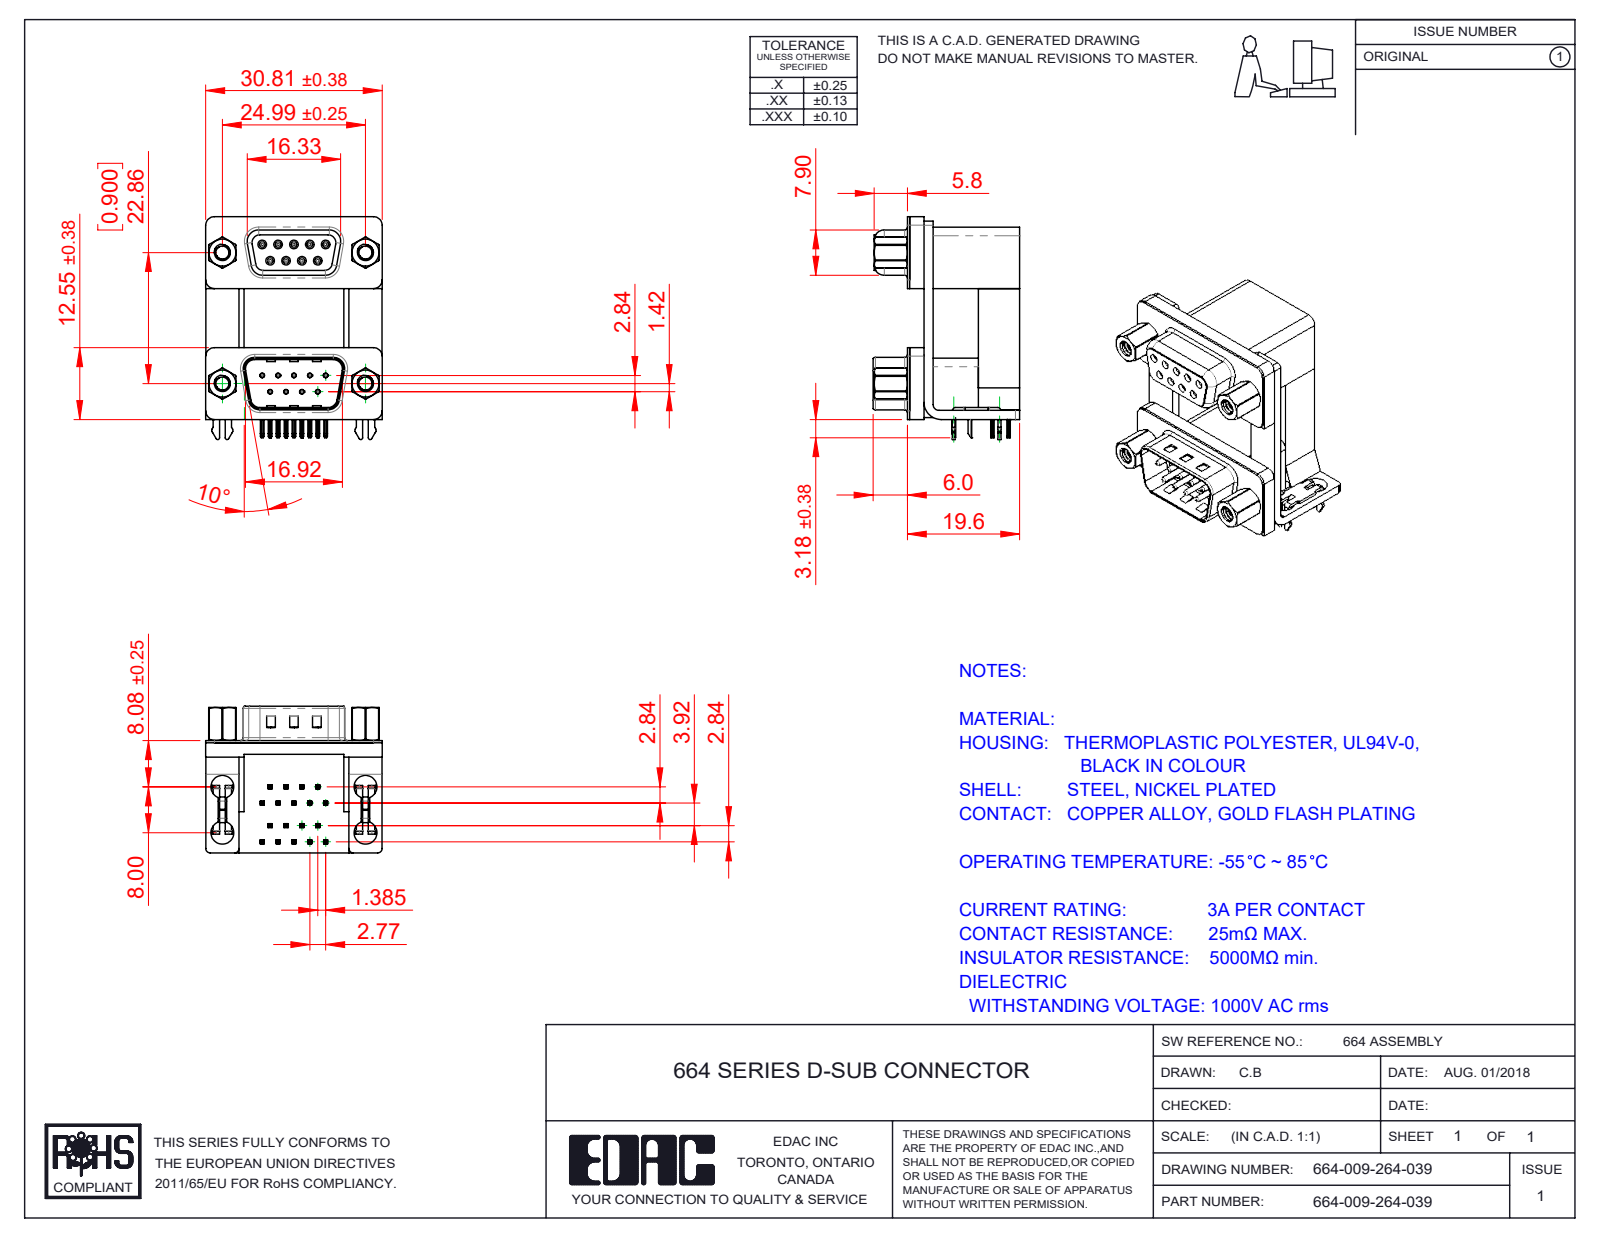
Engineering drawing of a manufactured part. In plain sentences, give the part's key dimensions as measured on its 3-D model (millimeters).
The part is named "664 Contact Bottom Lower; 664 2 Prong Board Lock_3; 664-009-264-039; 664 4-40 Hex Standoff 5 (+8 more)". Its 3-D file was written by "SolidWorks 2020 (CONFIG_CONTROL_DESIGN)". It is 35 solids with 2933 faces: 1409 planar, 889 cylindrical and 635 other. Overall it measures 38.91 by 30.81 by 25.6 millimeters. Its volume is 11 747 cubic millimeters and its surface area 14 269 square millimeters. Round holes: 18 of diameter 0.8, 9 of diameter 0.35, 9 of diameter 0.9, 8 of diameter 4, 4 of diameter 2.26, 4 of diameter 2.29, 4 of diameter 3.5, 4 of diameter 4.8, 4 of diameter 5. Round bosses or shafts: 9 of diameter 1.2, 9 of diameter 0.75, 4 of diameter 4.9, 4 of diameter 4.75, 4 of diameter 3.9, 4 of diameter 2.79. Partial cylindrical surfaces (rounded edges, fillets, slot ends): 74 of radius 0.1, 46 of radius 0.25, 36 of radius 0.15, 18 of radius 0.12, 18 of radius 0.35, 16 of radius 0.5, 13 of radius 1.5, 10 of radius 0.75. The main face-to-face distances are 0.4, 2.5, 16.7, 19.2, 12, 7.2, 9.5, 12.4, 1.6, 19.6. The hole center spacings are 3.16, 23.03, 2.77, 22.86, 23.52, 25.74, 5.54, 26.03.
